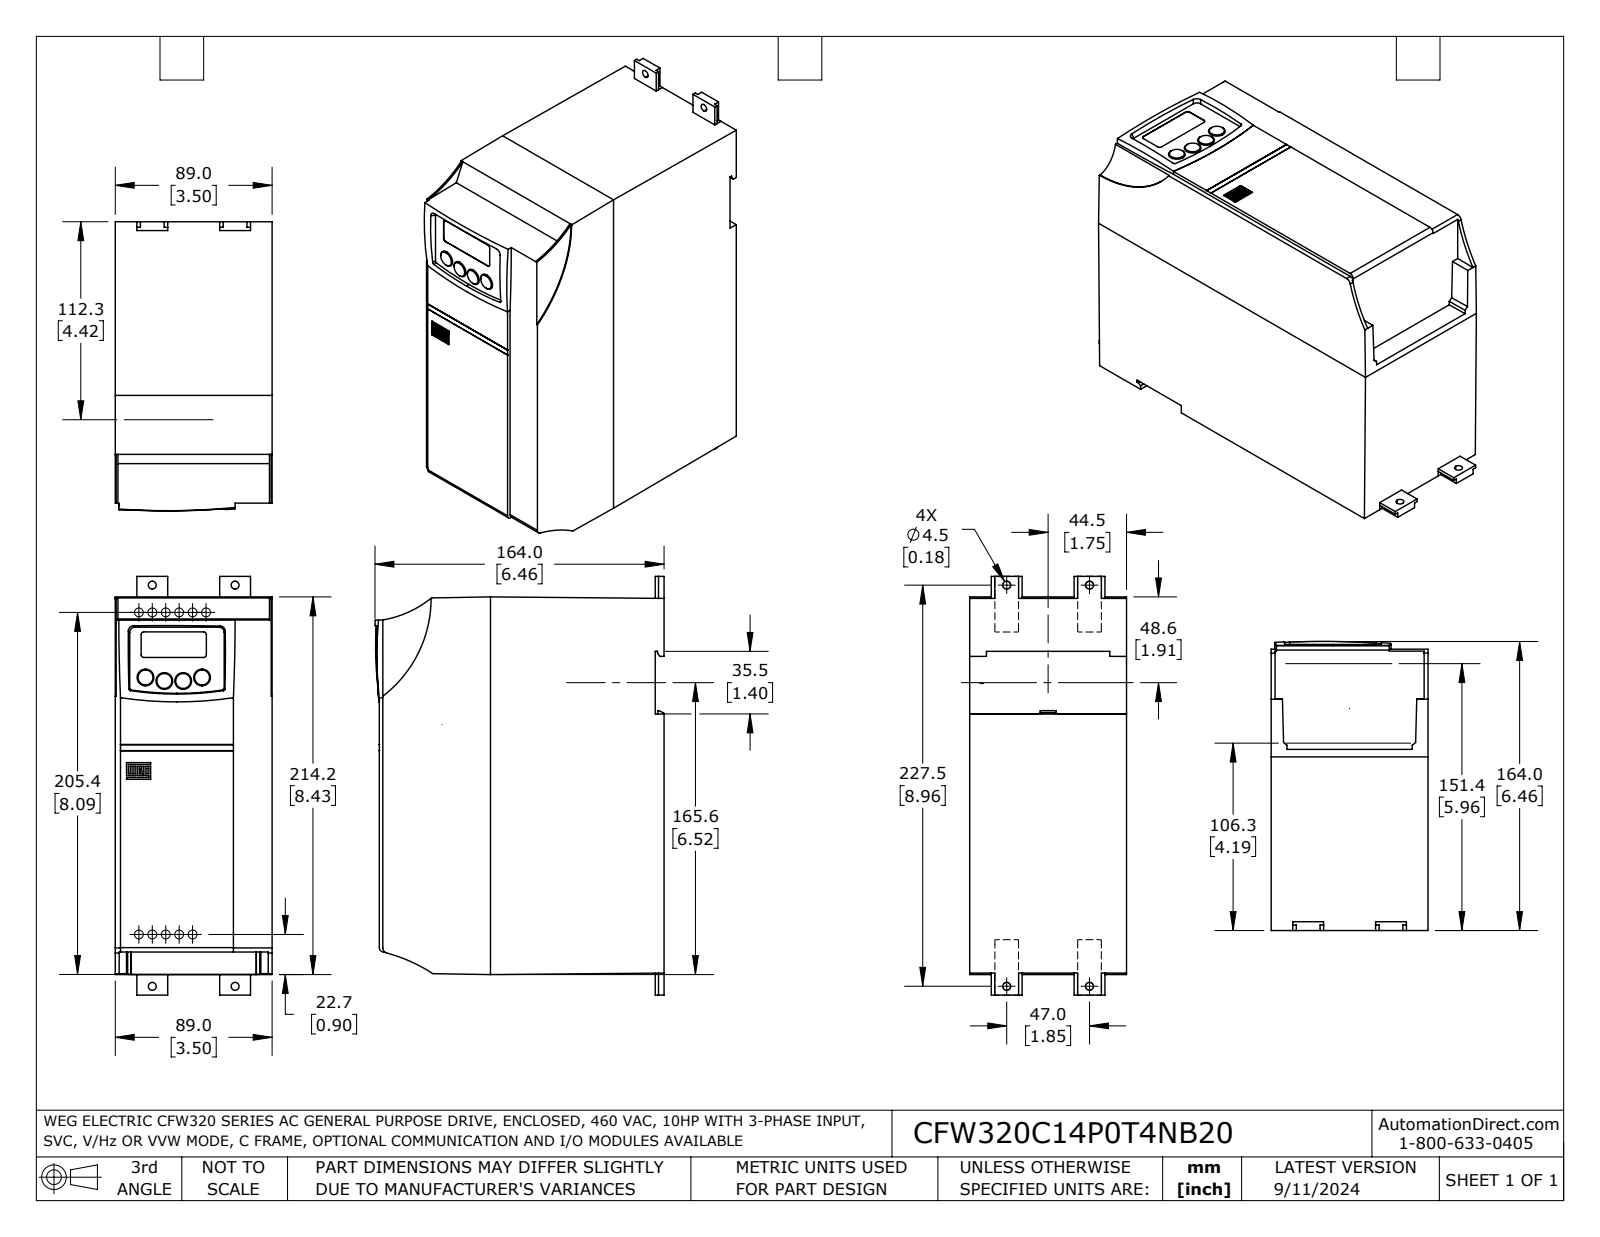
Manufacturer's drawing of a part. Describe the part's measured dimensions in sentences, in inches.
The part is named "CFW320C14P0T4NB20". Its 3-D file was written by "SolidWorks 2021 (AUTOMOTIVE_DESIGN)". It is 1 solid with 206 faces: 165 planar, 28 cylindrical and 13 other. Overall it measures 9.351 by 6.458 by 3.504 inches. Its volume is 180.5 cubic inches and its surface area 215.4 square inches. Round holes: 4 of diameter 0.177. Partial cylindrical surfaces (rounded edges, fillets, slot ends): 4 of radius 0.059, 3 of radius 0.118, 2 of radius 40.039, 1 of radius 0.039, 1 of radius 0.098, 1 of radius 2.362, 1 of radius 2.75, 1 of radius 3.543. The main face-to-face distances are 3.504, 6.362, 0.079, 6.283, 0.197, 6.087, 6.165, 0.039, 0.02, 3.484. The hole center spacings are 1.85, 8.961, 9.15.
